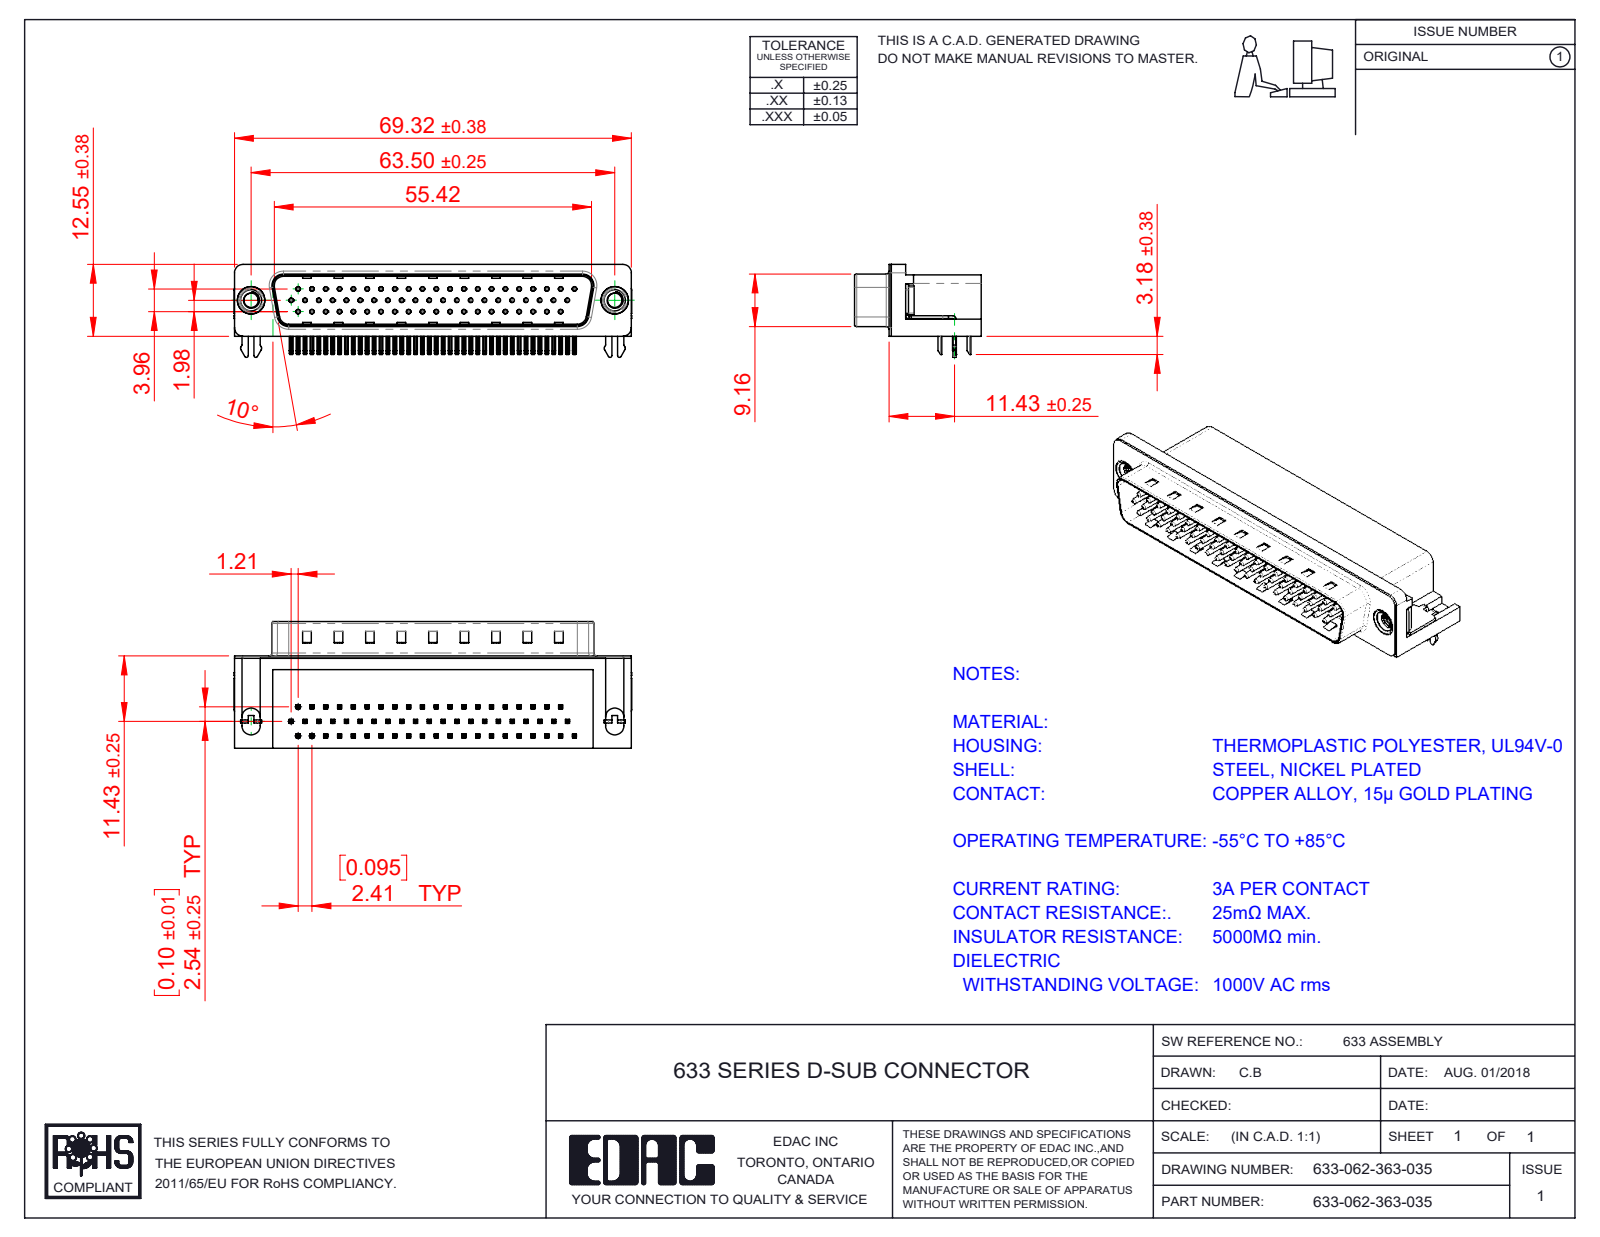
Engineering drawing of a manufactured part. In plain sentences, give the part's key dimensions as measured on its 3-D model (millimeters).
The part is named "633 Shell_62 Contact; 633 Housing_62 Contact; 633 Contact Middle; 633 Contact Top (+4 more)". Its 3-D file was written by "SolidWorks 2016 (CONFIG_CONTROL_DESIGN)". It is 68 solids with 5116 faces: 3245 planar, 1454 cylindrical and 417 other. Overall it measures 69.4 by 22.1 by 16.25 millimeters. Its volume is 11 048 cubic millimeters and its surface area 13 413 square millimeters. Round holes: 62 of diameter 0.35, 62 of diameter 0.8, 2 of diameter 2.5, 2 of diameter 4, 2 of diameter 4.8, 2 of diameter 5. Round bosses or shafts: 62 of diameter 0.75, 2 of diameter 4.9, 2 of diameter 4.75, 2 of diameter 3.9. Partial cylindrical surfaces (rounded edges, fillets, slot ends): 256 of radius 0.25, 124 of radius 0.12, 16 of radius 1, 14 of radius 0.5, 8 of radius 1.6, 7 of radius 1.5, 4 of radius 0.32, 4 of radius 0.9. The main face-to-face distances are 0.4, 10.35, 15.7, 8.76, 2.9, 2.5, 2.54, 2.1, 8.36, 16.1. The hole center spacings are 2.41, 4.82, 7.24, 9.65, 14.48, 16.89, 4.83, 7.23.
